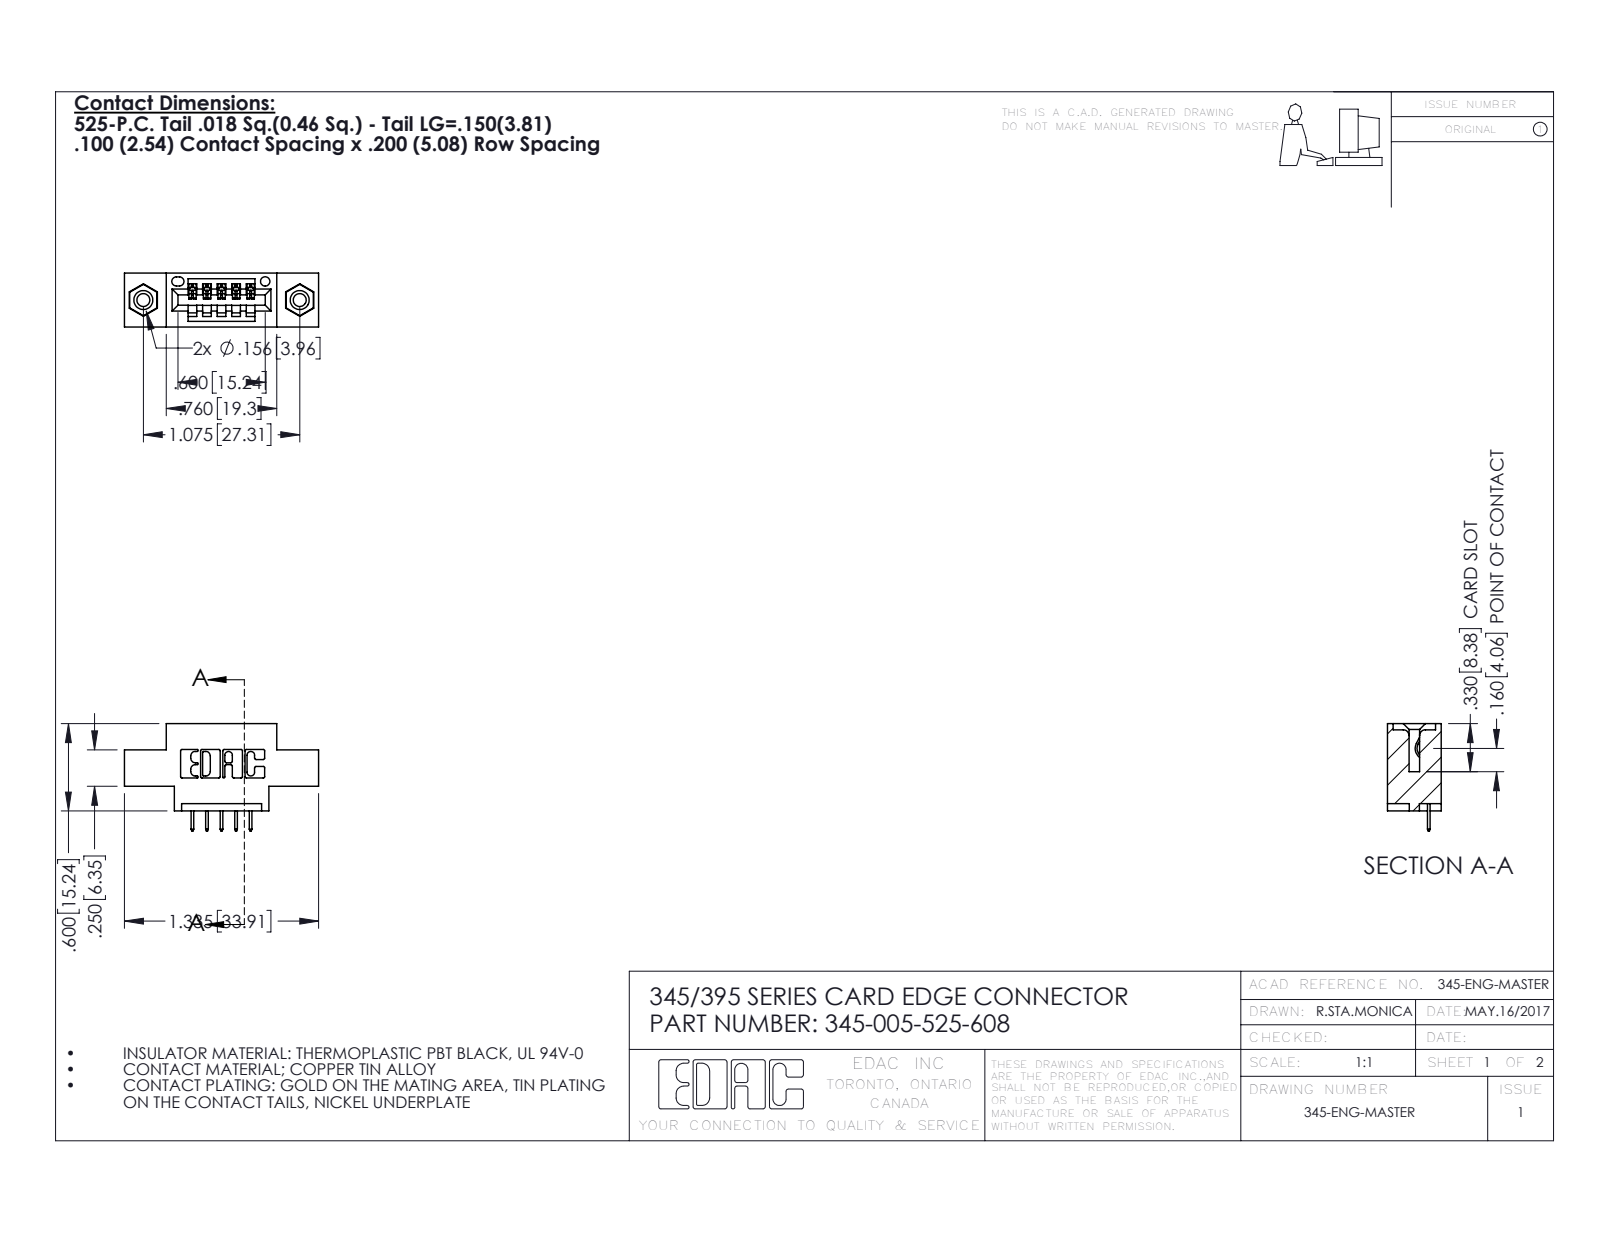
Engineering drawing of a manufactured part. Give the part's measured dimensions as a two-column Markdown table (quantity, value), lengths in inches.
| quantity | value |
| --- | --- |
| part name | 345-292-001_345-293-125; 345 Part_0.170 Offset - 0.156 Dia-TI; 345-005-525-608; 345-250-001_345-250-003-102 |
| STEP written by | SolidWorks 2020 (CONFIG_CONTROL_DESIGN) |
| units | inches |
| bodies | 8 solids, 500 faces (346 planar, 138 cylindrical, 16 other) |
| overall size | 1.335 × 0.737 × 0.37 |
| volume | 0.169 in³ |
| surface area | 5.062 in² |
| round holes (diameter × count) | 0.089 × 2, 0.125 × 2, 0.156 × 2, 0.064 × 1 |
| round bosses / shafts (diameter × count) | 0.155 × 2 |
| partial cylindrical surfaces (radius × count) | 0.01 × 22, 0.006 × 10, 0.007 × 6, 0.031 × 6, 0.026 × 3, 0.031 × 2, 0.04 × 2, 0.014 × 1 |
| main face-to-face distances | 0.37, 0.2, 0.1, 0.072, 0.298, 0.025, 0.25, 0.06, 0.55, 0.15 |
| hole center spacings | 0.27, 0.847, 1.075 |
